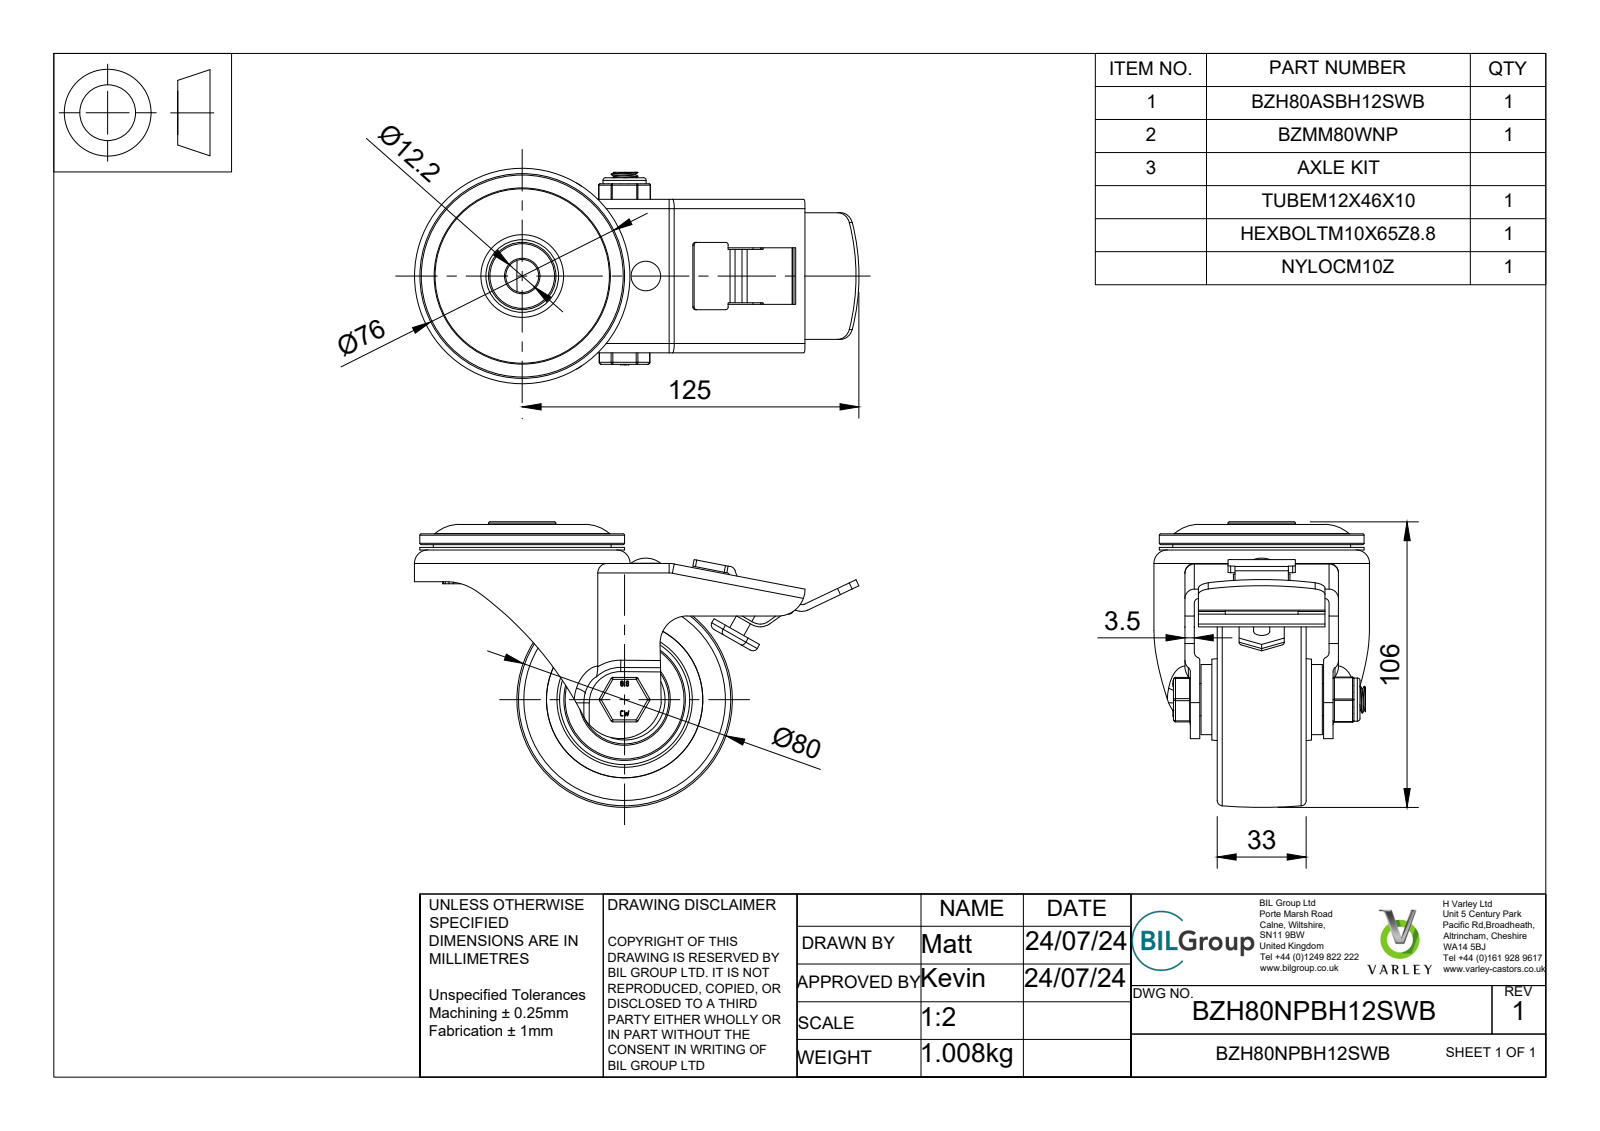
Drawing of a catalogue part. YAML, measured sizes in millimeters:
part_name: "BZH80NPBH12SWB v3; BZH80ASBH12SWB v1; ZINC PLATED, PRESSED STEEL TOP PLATE; ZINC PLATED, PRESSED STEEL FORKS (+7 more)"
step_written_by: "Autodesk Translation Framework v13.14.0.145 (AUTOMOTIVE_DESIGN)"
units: millimeters
bodies: {solids: 30, faces: 807, planar: 368, cylindrical: 285, other: 154}
overall_size: [165, 106, 80]
volume: 257955
surface_area: 121246
round_holes:
  - {diameter: 6, count: 2}
  - {diameter: 58, count: 2}
  - {diameter: 10, count: 1}
  - {diameter: 10.2, count: 1}
  - {diameter: 12, count: 1}
  - {diameter: 12.2, count: 1}
  - {diameter: 12.5, count: 1}
  - {diameter: 24, count: 1}
round_bosses_or_shafts:
  - {diameter: 76, count: 1}
  - {diameter: 66, count: 1}
  - {diameter: 59, count: 1}
  - {diameter: 49, count: 1}
  - {diameter: 35, count: 1}
  - {diameter: 26, count: 1}
  - {diameter: 25, count: 1}
  - {diameter: 22, count: 1}
partial_cylinders:
  - {radius: 0.5, count: 18}
  - {radius: 1, count: 14}
  - {radius: 0.75, count: 12}
  - {radius: 2, count: 11}
  - {radius: 1.75, count: 10}
  - {radius: 3.5, count: 8}
  - {radius: 2.5, count: 6}
  - {radius: 5, count: 5}
face_to_face_distances: [3.5, 1, 2, 4, 6, 8.5, 5, 2.5, 13.5, 9.5]
hole_center_spacings: [45.89]
